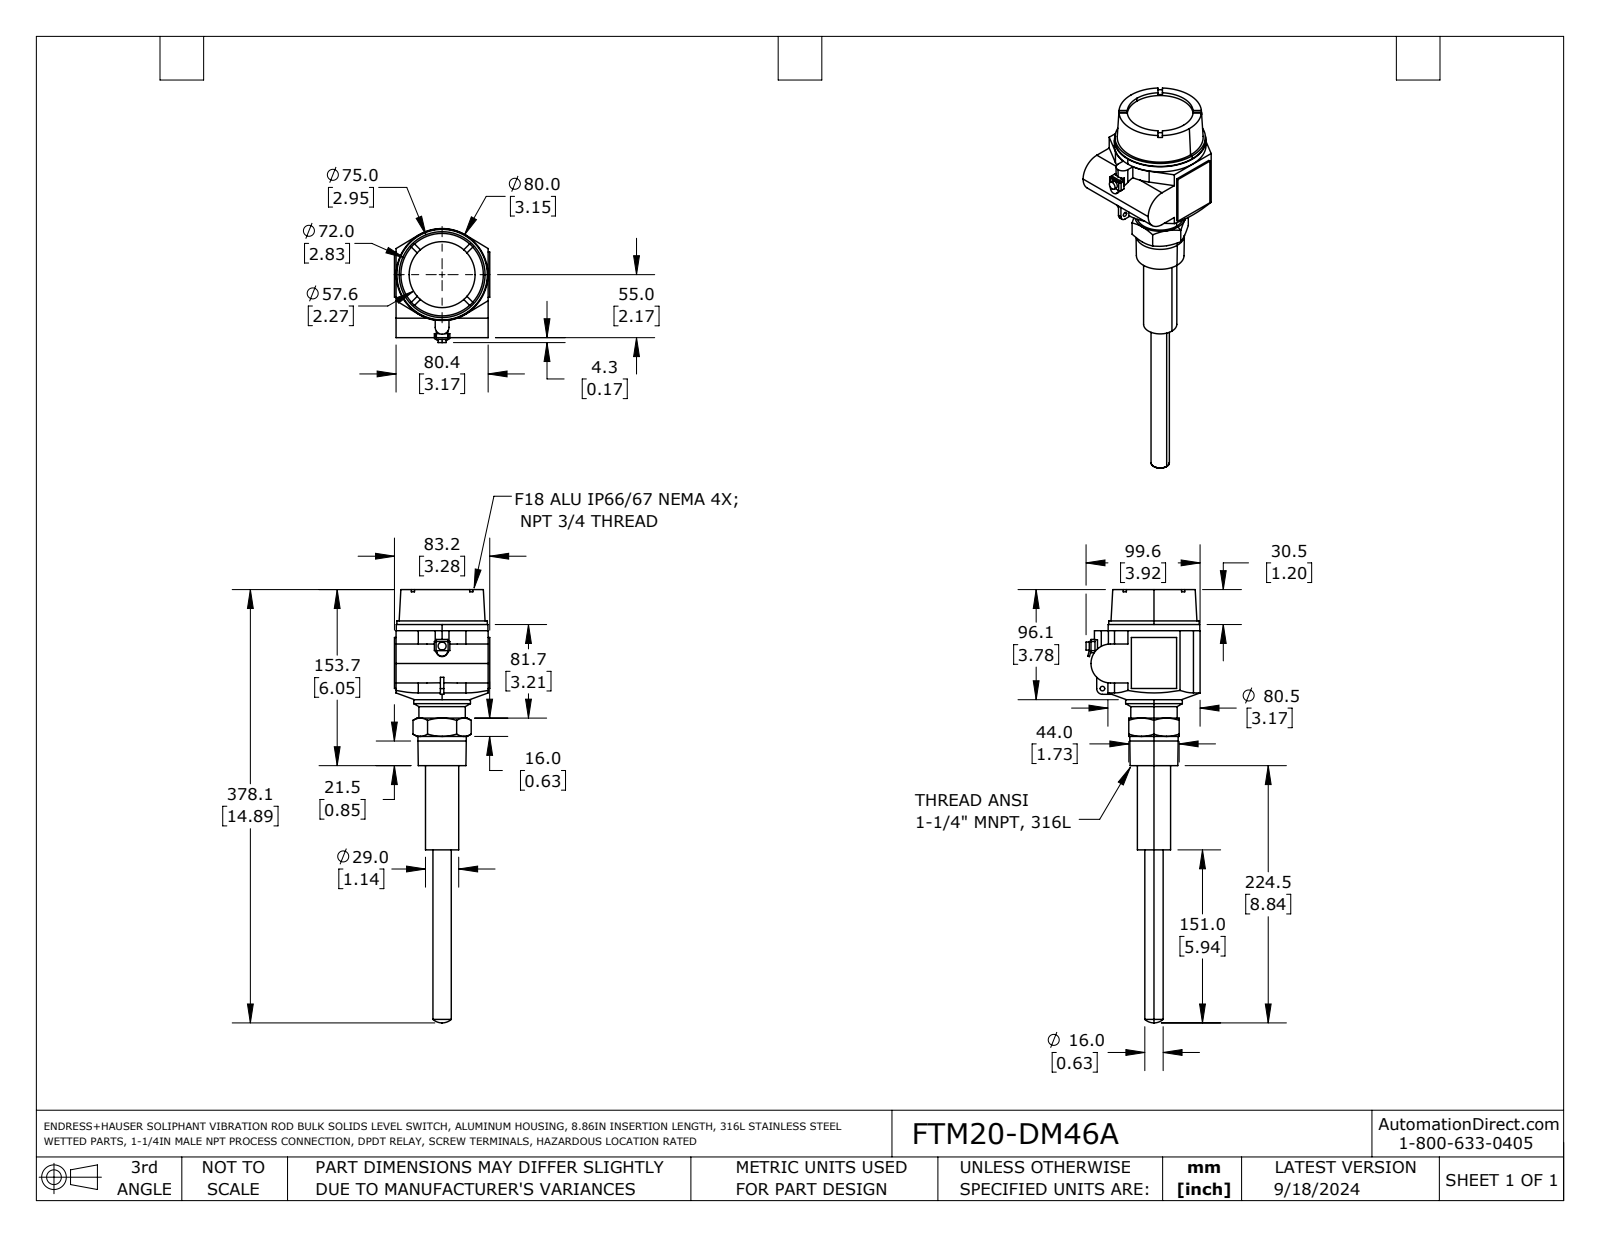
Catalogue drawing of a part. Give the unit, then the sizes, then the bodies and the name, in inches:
Units: inches
Overall size (bounding box): 14.888 × 3.919 × 3.276
Round holes (diameter × count): ⌀0.157 ×1, ⌀2.268 ×1
Round bosses / shafts (diameter × count): ⌀3.15 ×1, ⌀3.11 ×1, ⌀1.949 ×1, ⌀1.661 ×1, ⌀1.594 ×1, ⌀1.142 ×1, ⌀0.63 ×1, ⌀0.276 ×1
Partial cylindrical surfaces — rounded edges, fillets, slot ends (radius × count): R0.059 ×3, R0.197 ×2, R0.236 ×1, R0.669 ×1, R1.585 ×1
Main face-to-face distances: 0.055, 3.22, 3.276, 3.165, 0.118, 1.732, 3.169, 5.931, 6.049, 4.636
Volume: 41.75 in³ · Surface area: 96.75 in²
Bodies: 1 solid, 151 faces (88 planar, 36 cylindrical, 27 other)
Part name (STEP PRODUCT): FTM20-DM46A
STEP written by: SolidWorks 2021 (AUTOMOTIVE_DESIGN)
